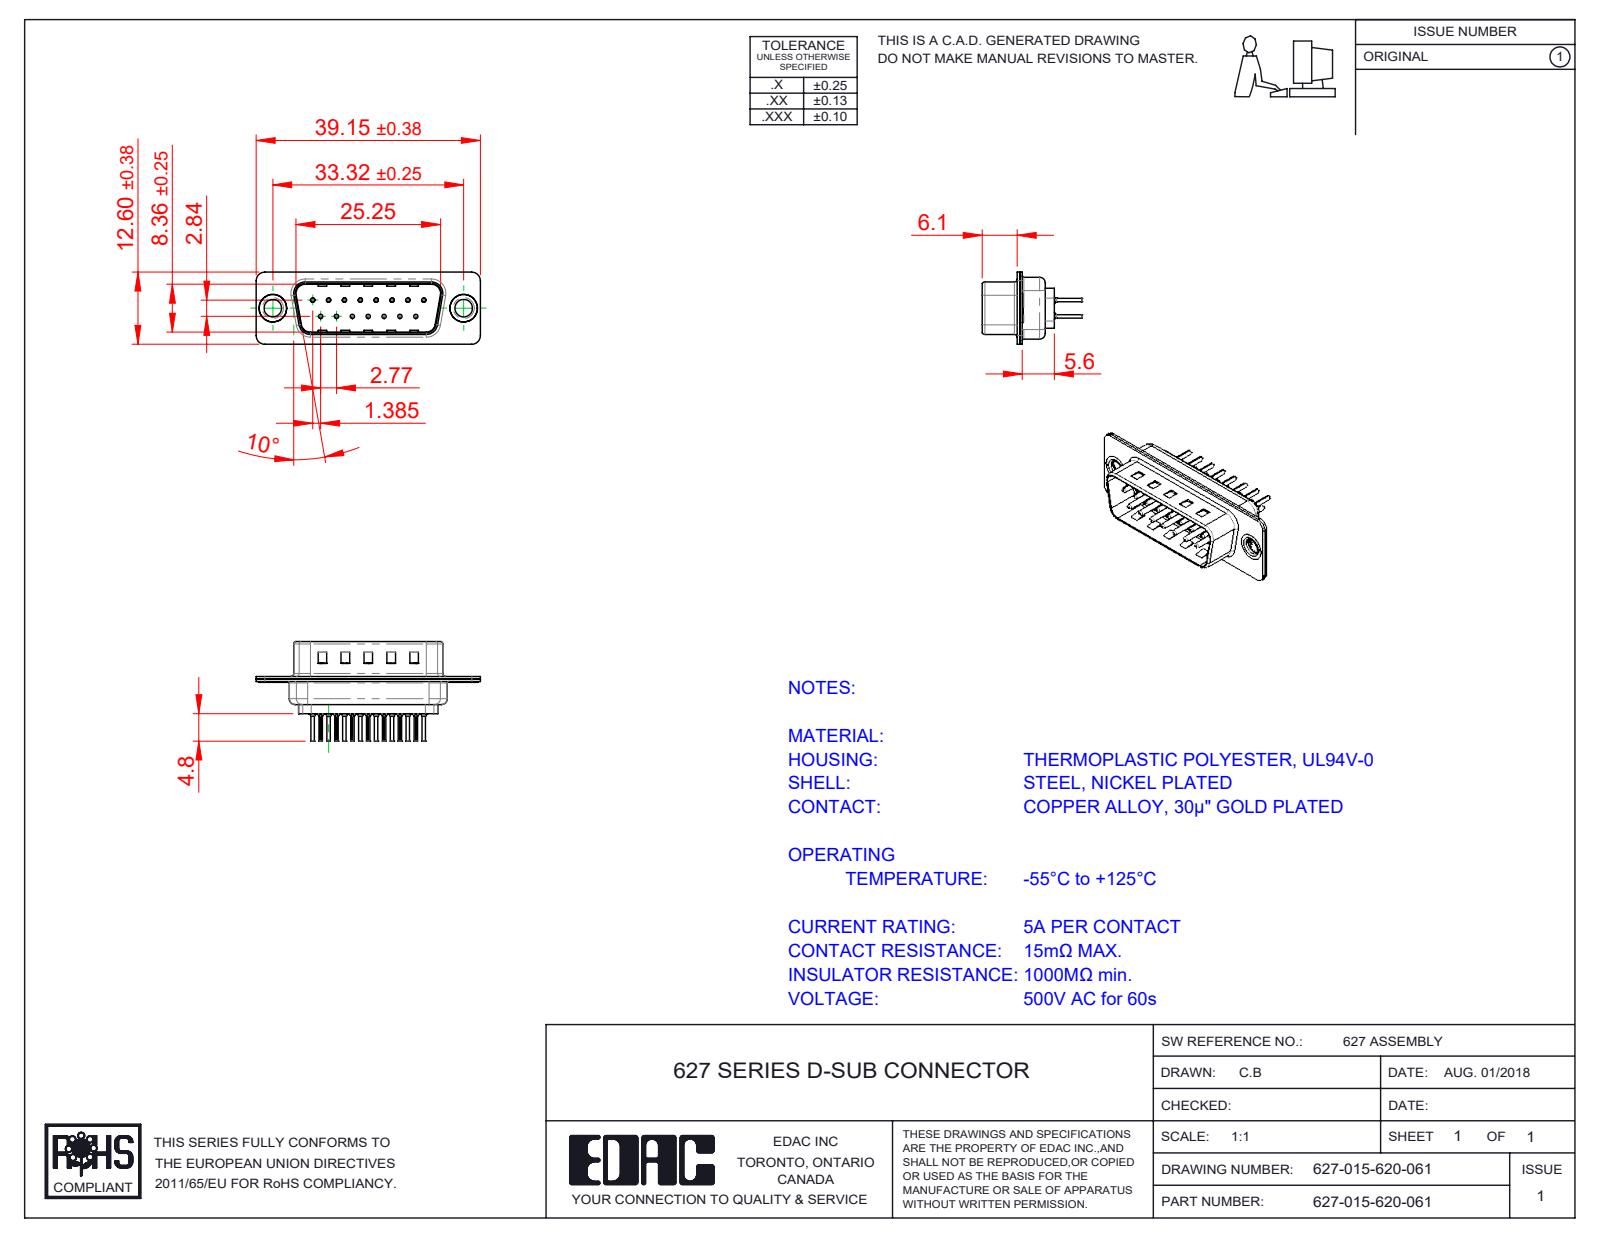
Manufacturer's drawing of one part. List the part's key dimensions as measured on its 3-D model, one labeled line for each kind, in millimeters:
Part name (STEP PRODUCT): 627 Contact Row 2_20L; 627 Thru Hole Rivet; 627 Shell Rear_15 Contacts; 627-015-620-061 (+3 more)
STEP written by: SolidWorks 2020 (CONFIG_CONTROL_DESIGN)
Units: millimetres
Bodies: 20 solids, 1784 faces (499 planar, 672 cylindrical, 613 other)
Overall size (bounding box): 39.15 × 17.3 × 12.6
Volume: 1 753 mm³ · Surface area: 5 247 mm²
Round holes (diameter × count): ⌀0.2 ×15, ⌀0.35 ×15, ⌀1.1 ×15, ⌀1.6 ×15, ⌀3.05 ×2, ⌀4 ×2, ⌀4.8 ×2
Round bosses / shafts (diameter × count): ⌀2 ×15, ⌀1.5 ×15, ⌀0.75 ×15, ⌀0.6 ×15, ⌀5 ×2, ⌀4.9 ×2, ⌀3.55 ×2
Partial cylindrical surfaces — rounded edges, fillets, slot ends (radius × count): R0.1 ×30, R1.5 ×16, R2 ×12, R0.5 ×8, R1.6 ×8, R0.25 ×4, R0.6 ×4, R0.65 ×4
Main face-to-face distances: 0.4, 0.45, 0.9, 0.82, 9.58, 8.76, 1.5, 1.4, 0.5, 6.5
Hole centre spacings: 3.16, 2.77, 5.54, 8.31, 11.08, 5.03, 5.04, 7.48
